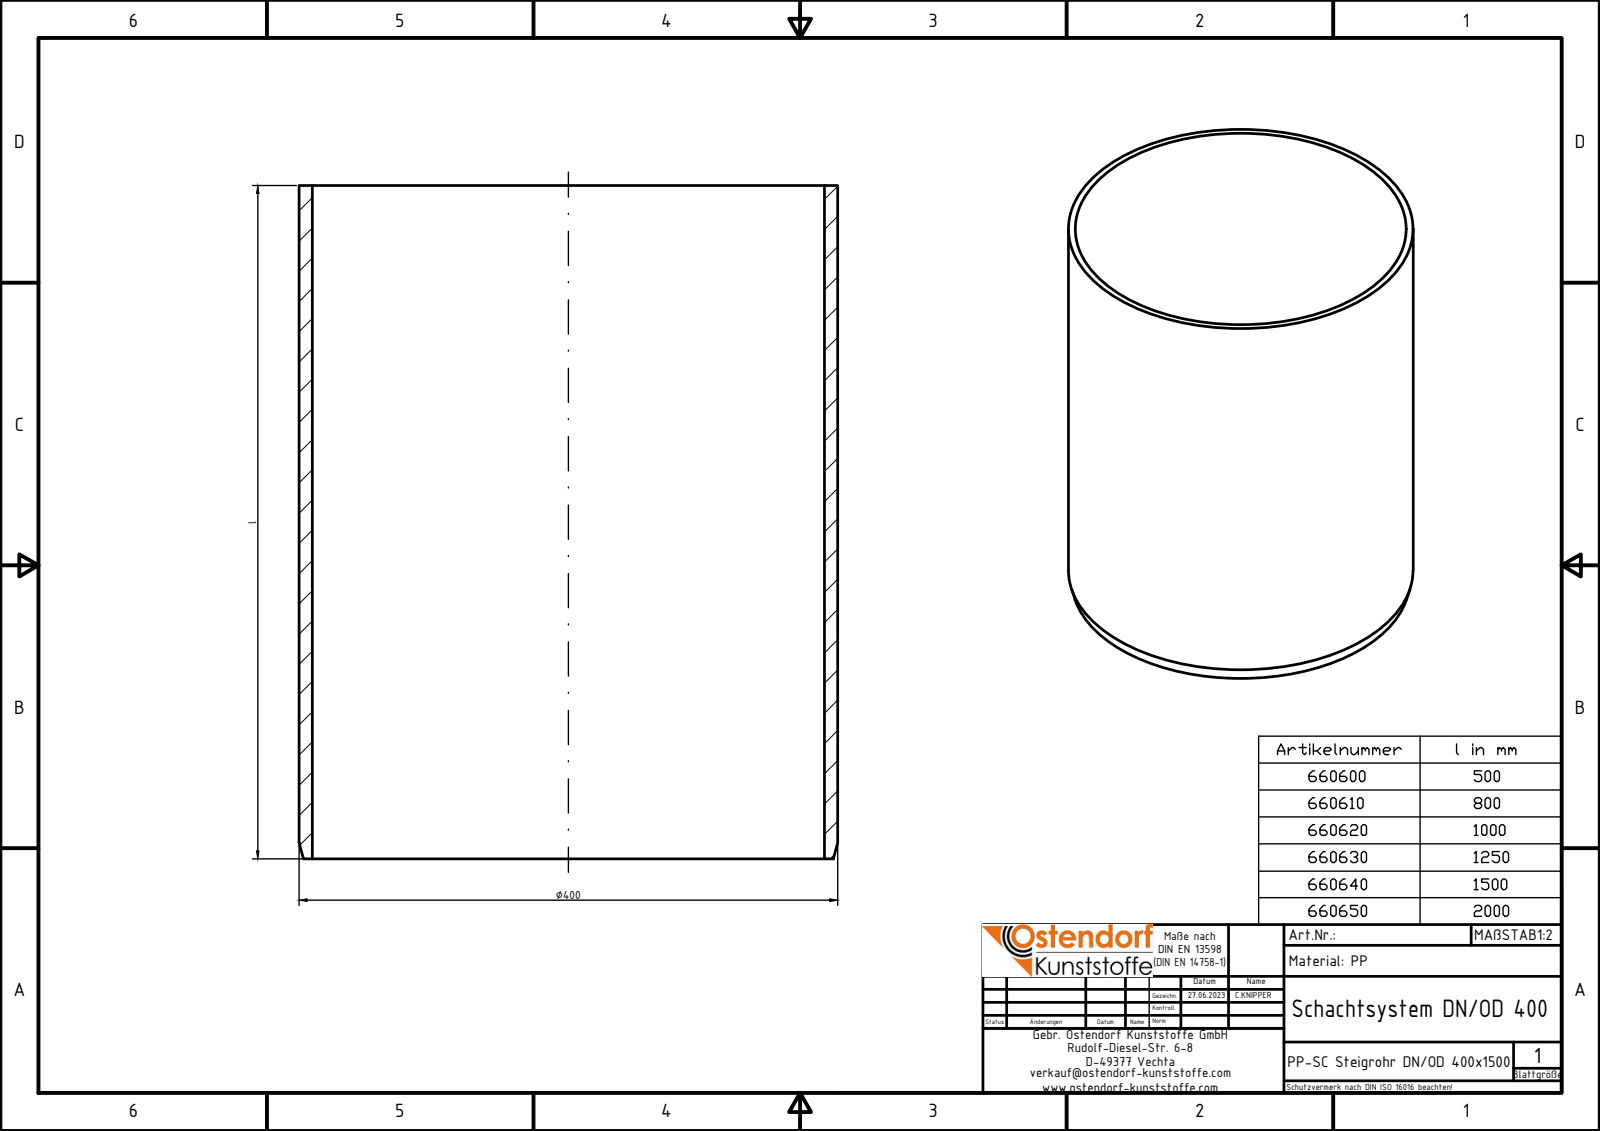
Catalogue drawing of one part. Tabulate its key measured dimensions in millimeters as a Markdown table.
| quantity | value |
| --- | --- |
| part name | 660640 |
| STEP written by | Autodesk Inventor 2020 (AUTOMOTIVE_DESIGN) |
| units | millimeters |
| bodies | 1 solid, 5 faces (2 planar, 2 cylindrical, 1 other) |
| overall size | 1500 × 400 × 400 |
| volume | 18 000 000 mm³ |
| surface area | 3 698 000 mm² |
| round holes (diameter × count) | 380.4 × 1 |
| round bosses / shafts (diameter × count) | 400 × 1 |
| main face-to-face distances | 1500 |
